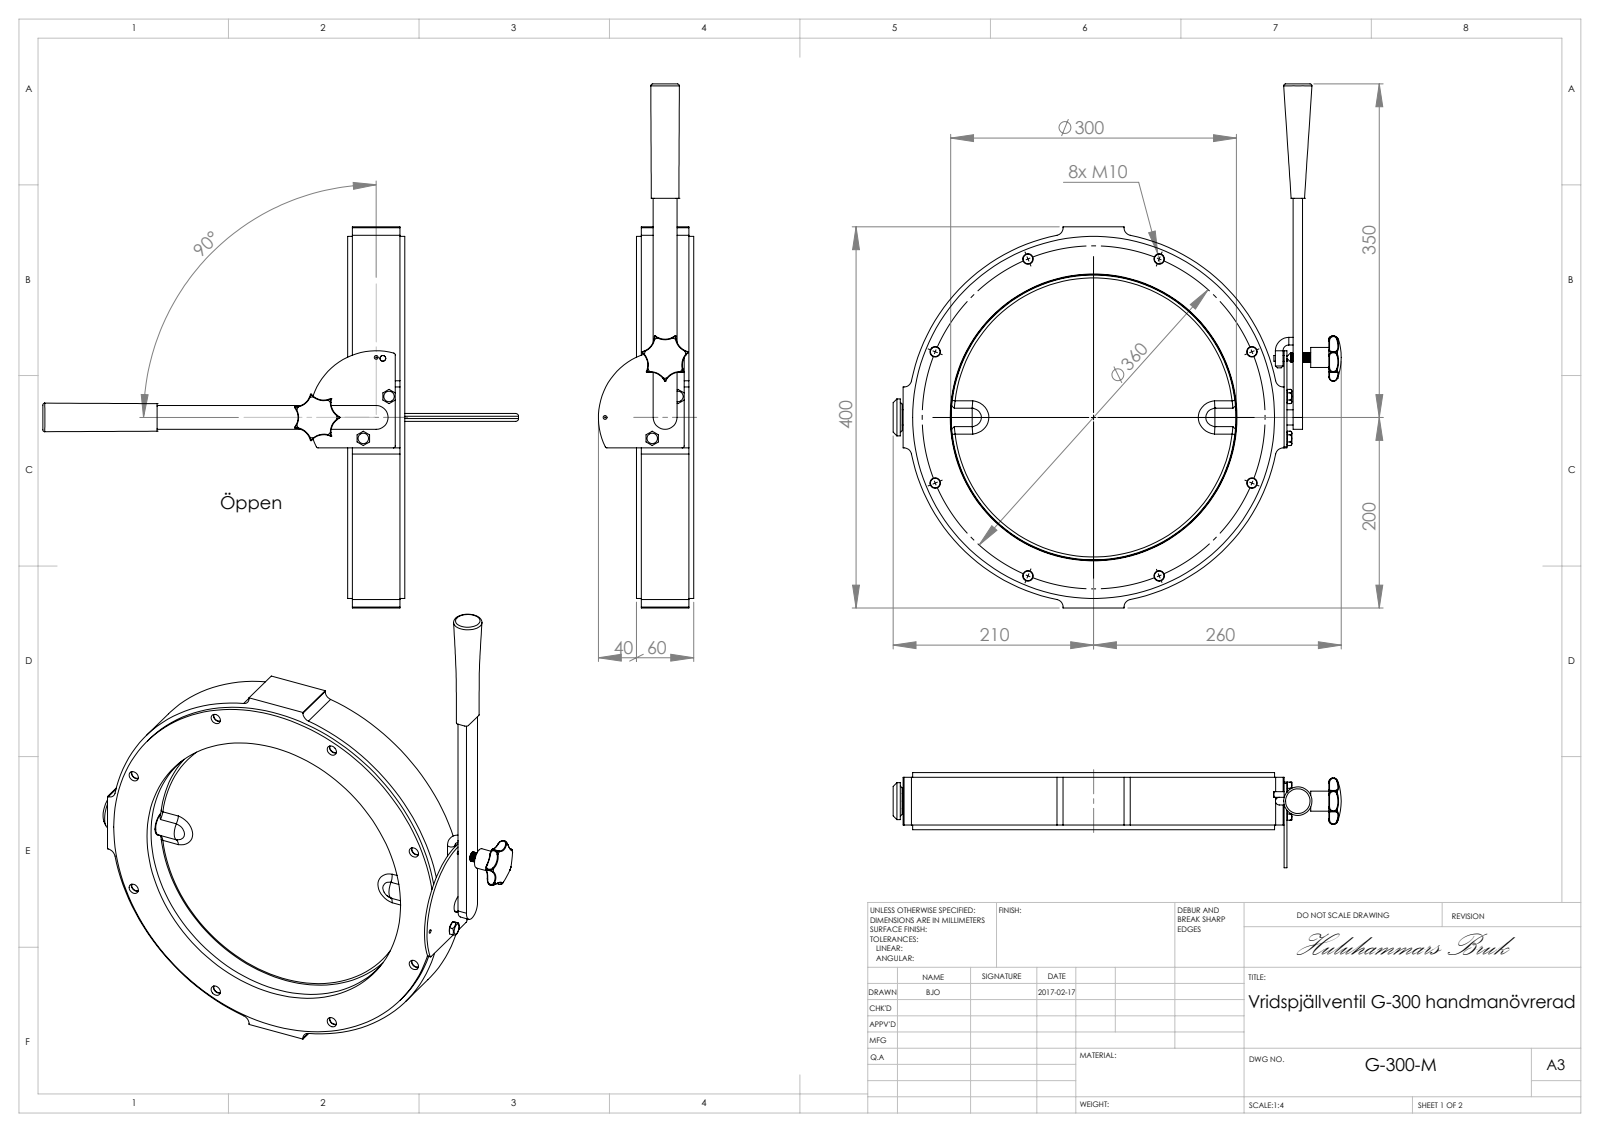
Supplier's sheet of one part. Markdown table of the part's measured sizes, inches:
| quantity | value |
| --- | --- |
| part name | G-300-M; pin-6x14; Skruv M6S 8x25; Vred-WN450-A4-50-M10x25_Vred-WN450-A4-50-M10x25-Wiberg (+4 more) |
| STEP written by | SolidWorks 2011 (AUTOMOTIVE_DESIGN) |
| units | inches |
| bodies | 8 solids, 289 faces (76 planar, 111 cylindrical, 102 other) |
| overall size | 21.654 × 18.522 × 3.937 |
| volume | 224.8 in³ |
| surface area | 1 090 in² |
| round holes (diameter × count) | 0.394 × 8, 0.433 × 8, 0.315 × 4, 0.354 × 2, 0.236 × 1, 0.63 × 1, 0.709 × 1, 1.024 × 1, 1.104 × 1, 11.811 × 1, 12.283 × 1 |
| round bosses / shafts (diameter × count) | 0.512 × 2, 0.315 × 2, 14.961 × 1, 11.768 × 1, 1.528 × 1, 0.984 × 1, 0.827 × 1, 0.394 × 1 |
| partial cylindrical surfaces (radius × count) | 0.315 × 8, 0.656 × 7, 0.394 × 4, 0.079 × 3, 2.756 × 1, 7.677 × 1 |
| main face-to-face distances | 0.821, 1.148, 0.197, 1.018, 1.344, 2.165, 1.969, 0.327, 2.362, 0.118 |
| hole center spacings | 7.087, 10.022, 1.016, 5.424, 5.424, 13.094, 13.094, 14.173 |
